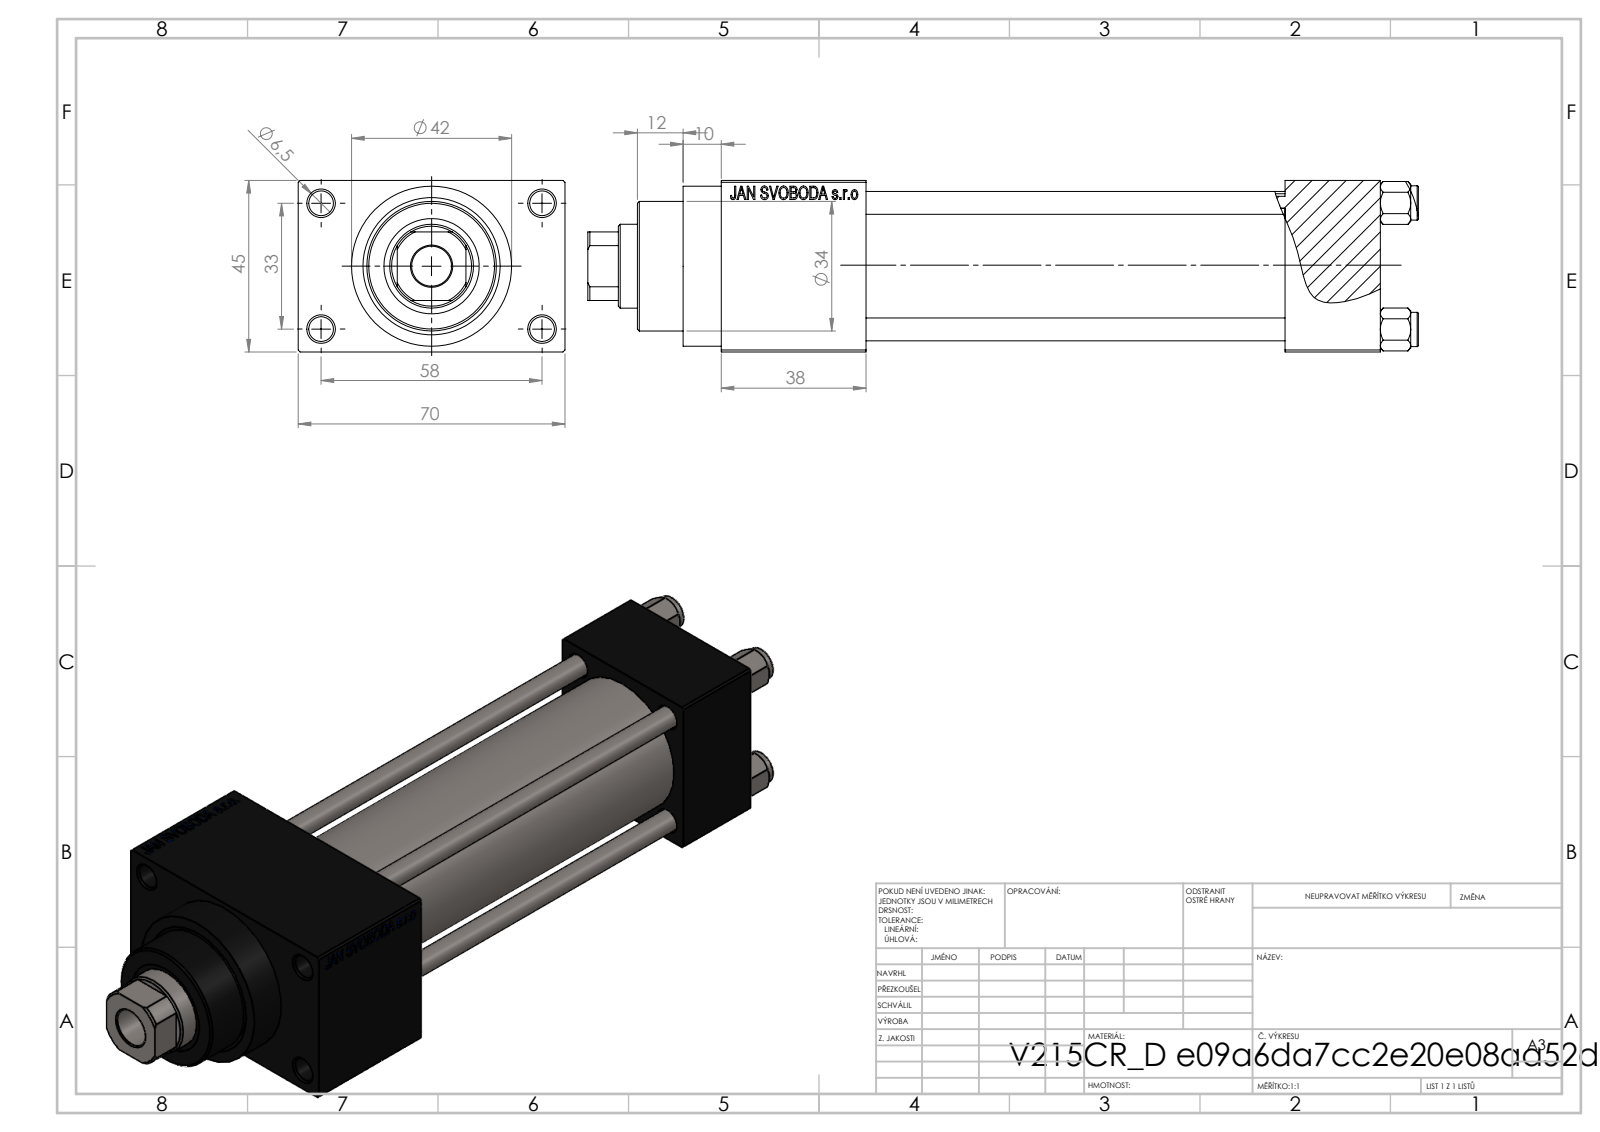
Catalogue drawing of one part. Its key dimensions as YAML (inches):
part_name: "V215CR_D_Body; NUT_M5_D; V215_VC_A; V215CR_D_TYCINKA (+1 more)"
step_written_by: "SolidWorks 2019 (CONFIG_CONTROL_DESIGN)"
units: inches
bodies: {solids: 11, faces: 1104, planar: 496, cylindrical: 88, other: 520}
overall_size: [8.583, 2.756, 1.772]
volume: 17.83
surface_area: 157.7
round_holes:
  - {diameter: 0.236, count: 4}
  - {diameter: 0.256, count: 4}
  - {diameter: 0.276, count: 2}
  - {diameter: 0.518, count: 2}
  - {diameter: 0.787, count: 2}
  - {diameter: 0.413, count: 1}
  - {diameter: 0.866, count: 1}
  - {diameter: 0.945, count: 1}
  - {diameter: 0.984, count: 1}
  - {diameter: 1.26, count: 1}
  - {diameter: 1.299, count: 1}
round_bosses_or_shafts:
  - {diameter: 0.354, count: 4}
  - {diameter: 1.654, count: 1}
  - {diameter: 1.496, count: 1}
  - {diameter: 1.339, count: 1}
partial_cylinders:
  - {radius: 0.413, count: 1}
face_to_face_distances: [1.772, 0.984, 0.492, 4.331, 5.315, 2.264, 5.827, 1.496, 6.811, 2.756]
hole_center_spacings: [0.488, 0.924, 1.307, 1.314, 1.392, 1.795, 2.219, 1.299]
